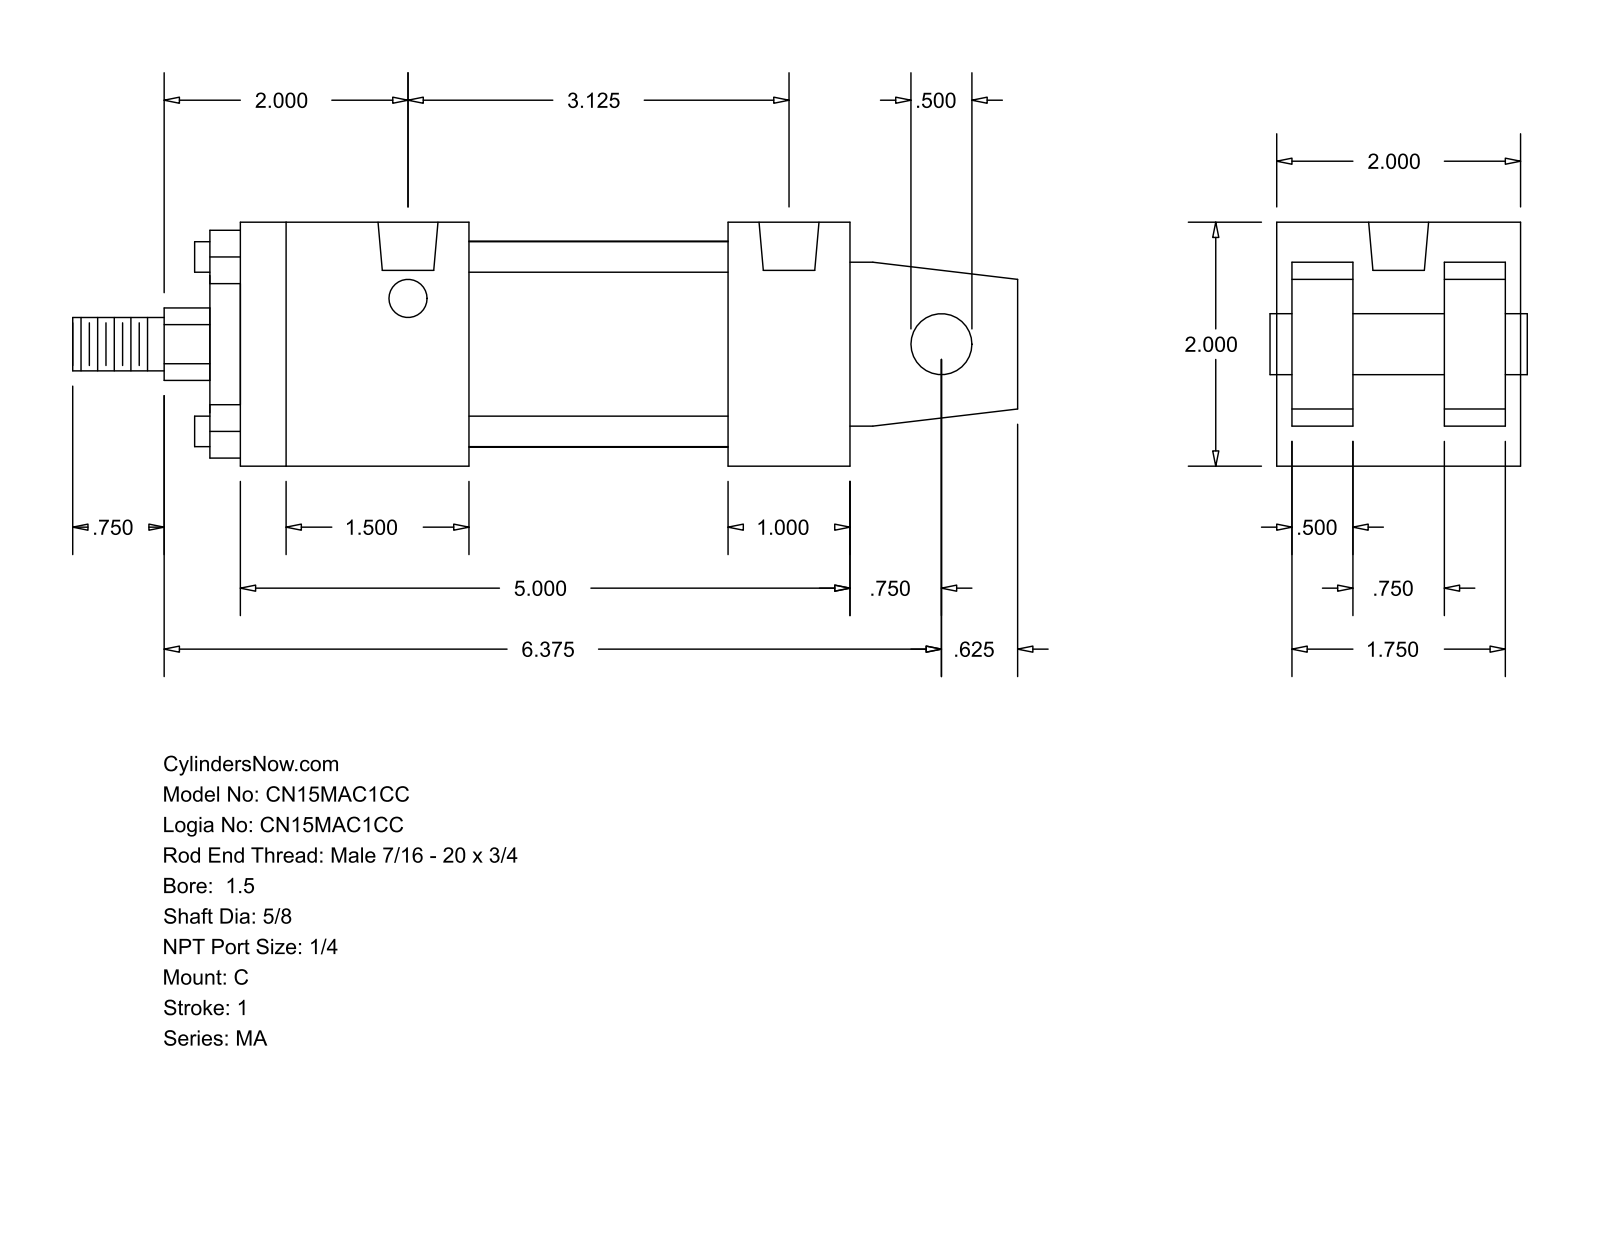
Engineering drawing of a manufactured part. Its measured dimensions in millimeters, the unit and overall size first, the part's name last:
Units: millimetres
Overall size (bounding box): 196.85 × 50.8 × 50.8
Round holes (diameter × count): ⌀7.94 ×4, ⌀12.49 ×2
Round bosses / shafts (diameter × count): ⌀6.35 ×4, ⌀42.93 ×1, ⌀28.57 ×1, ⌀15.88 ×1, ⌀12.7 ×1, ⌀11.11 ×1
Partial cylindrical surfaces — rounded edges, fillets, slot ends (radius × count): R7.54 ×1
Main face-to-face distances: 50.8, 12.7, 34.93, 15.87, 3.17, 47.63, 31.76, 53.97, 127, 101.59
Hole centre spacings: 79.38
Bodies: 0 solids, 103 faces (76 planar, 27 cylindrical, 0 other)
Part name (STEP PRODUCT): MA_C__0150_0.625
STEP written by: GSSL Pune (CONFIG_CONTROL_DESIGN)
